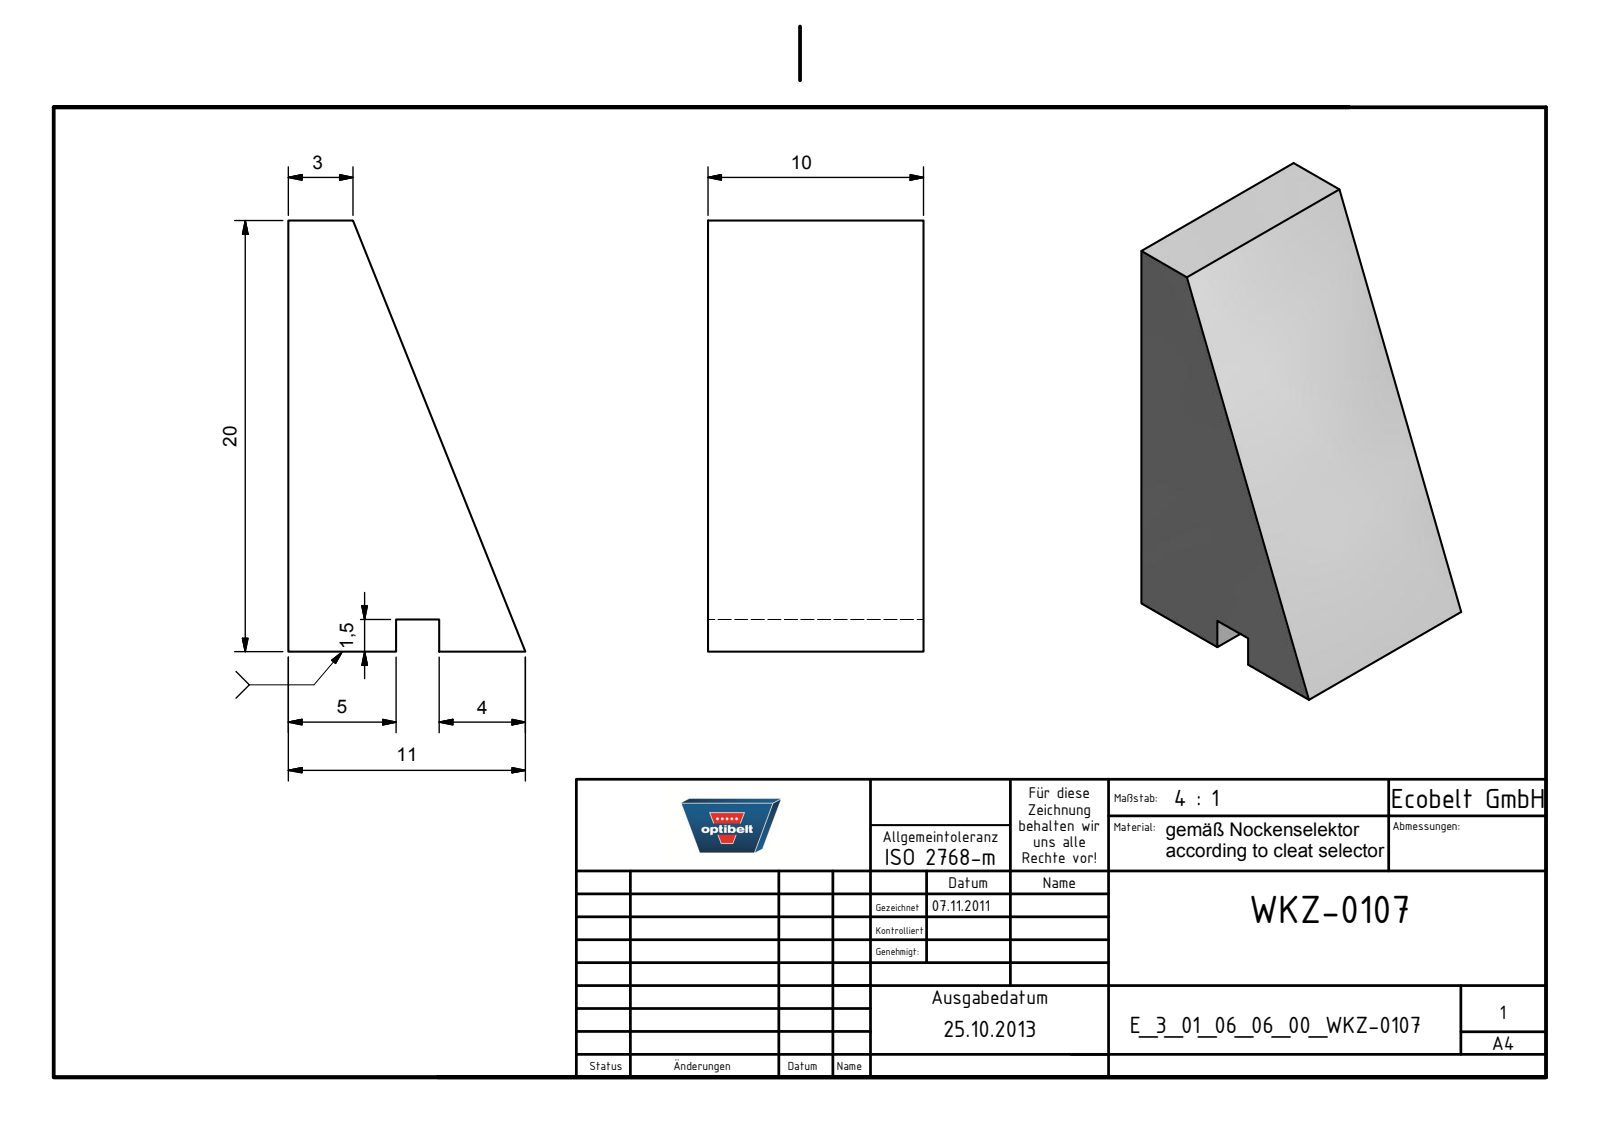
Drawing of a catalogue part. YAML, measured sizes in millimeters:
part_name: "E_3_01_06_06_00_WKZ-0107"
step_written_by: "Autodesk Inventor 2025 (AUTOMOTIVE_DESIGN)"
units: millimeters
bodies: {solids: 1, faces: 10, planar: 10, cylindrical: 0, other: 0}
overall_size: [20, 11, 10]
volume: 1370
surface_area: 859
face_to_face_distances: [10, 20, 1.5, 18.5, 7, 5, 2]
